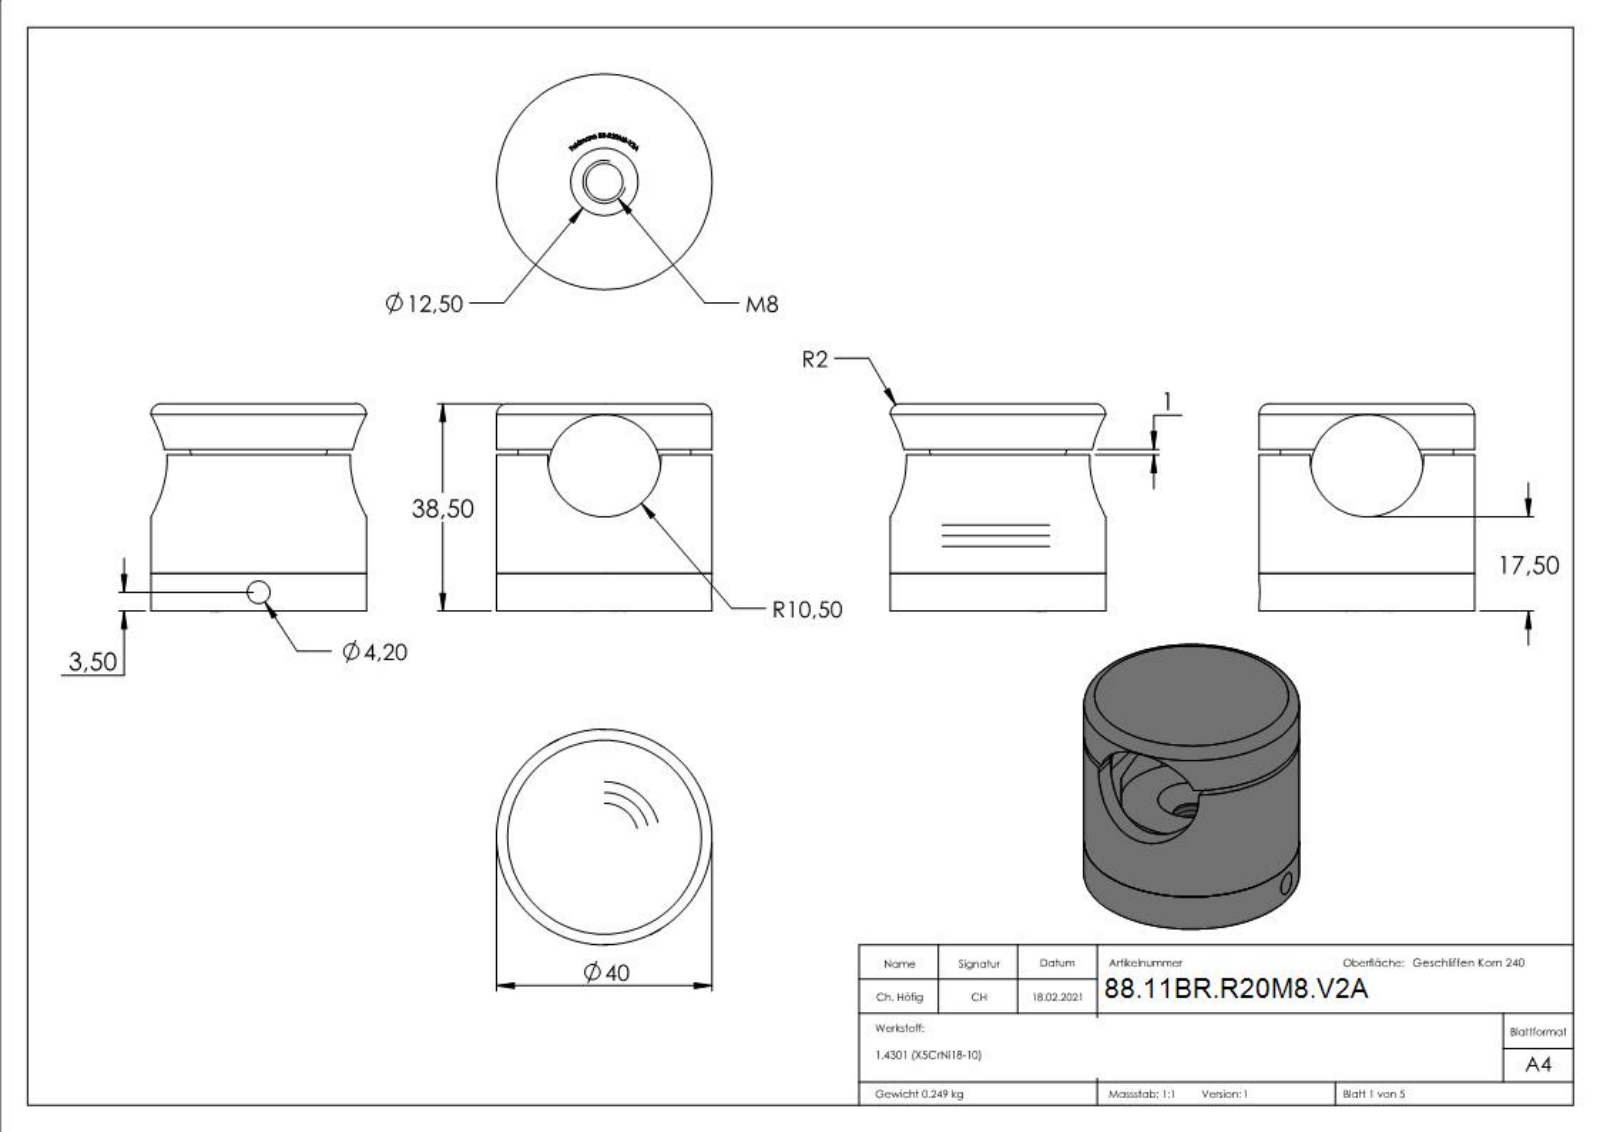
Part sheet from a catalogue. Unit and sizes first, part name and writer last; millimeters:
Units: millimetres
Overall size (bounding box): 64.34 × 40 × 40
Round holes (diameter × count): ⌀4.2 ×1, ⌀6.8 ×1, ⌀12.5 ×1, ⌀32.5 ×1
Round bosses / shafts (diameter × count): ⌀40 ×1, ⌀28 ×1
Partial cylindrical surfaces — rounded edges, fillets, slot ends (radius × count): R10.5 ×2, R13.25 ×1, R16.05 ×1
Main face-to-face distances: 7, 38.5, 31.5, 16, 9, 22.5, 30, 23, 14, 8.5
Volume: 31 485 mm³ · Surface area: 15 505 mm²
Bodies: 3 solids, 337 faces (187 planar, 23 cylindrical, 127 other)
Part name (STEP PRODUCT): BR-R1XM8-XXX Teil1_BR-2XM8-V2A Teil1; BR-R20M8-V2A; BR-R1XM8-XXX Teil1; BR-R1XM8-XXX Teil3 (+3 more)
STEP written by: SolidWorks 2018 (CONFIG_CONTROL_DESIGN)
